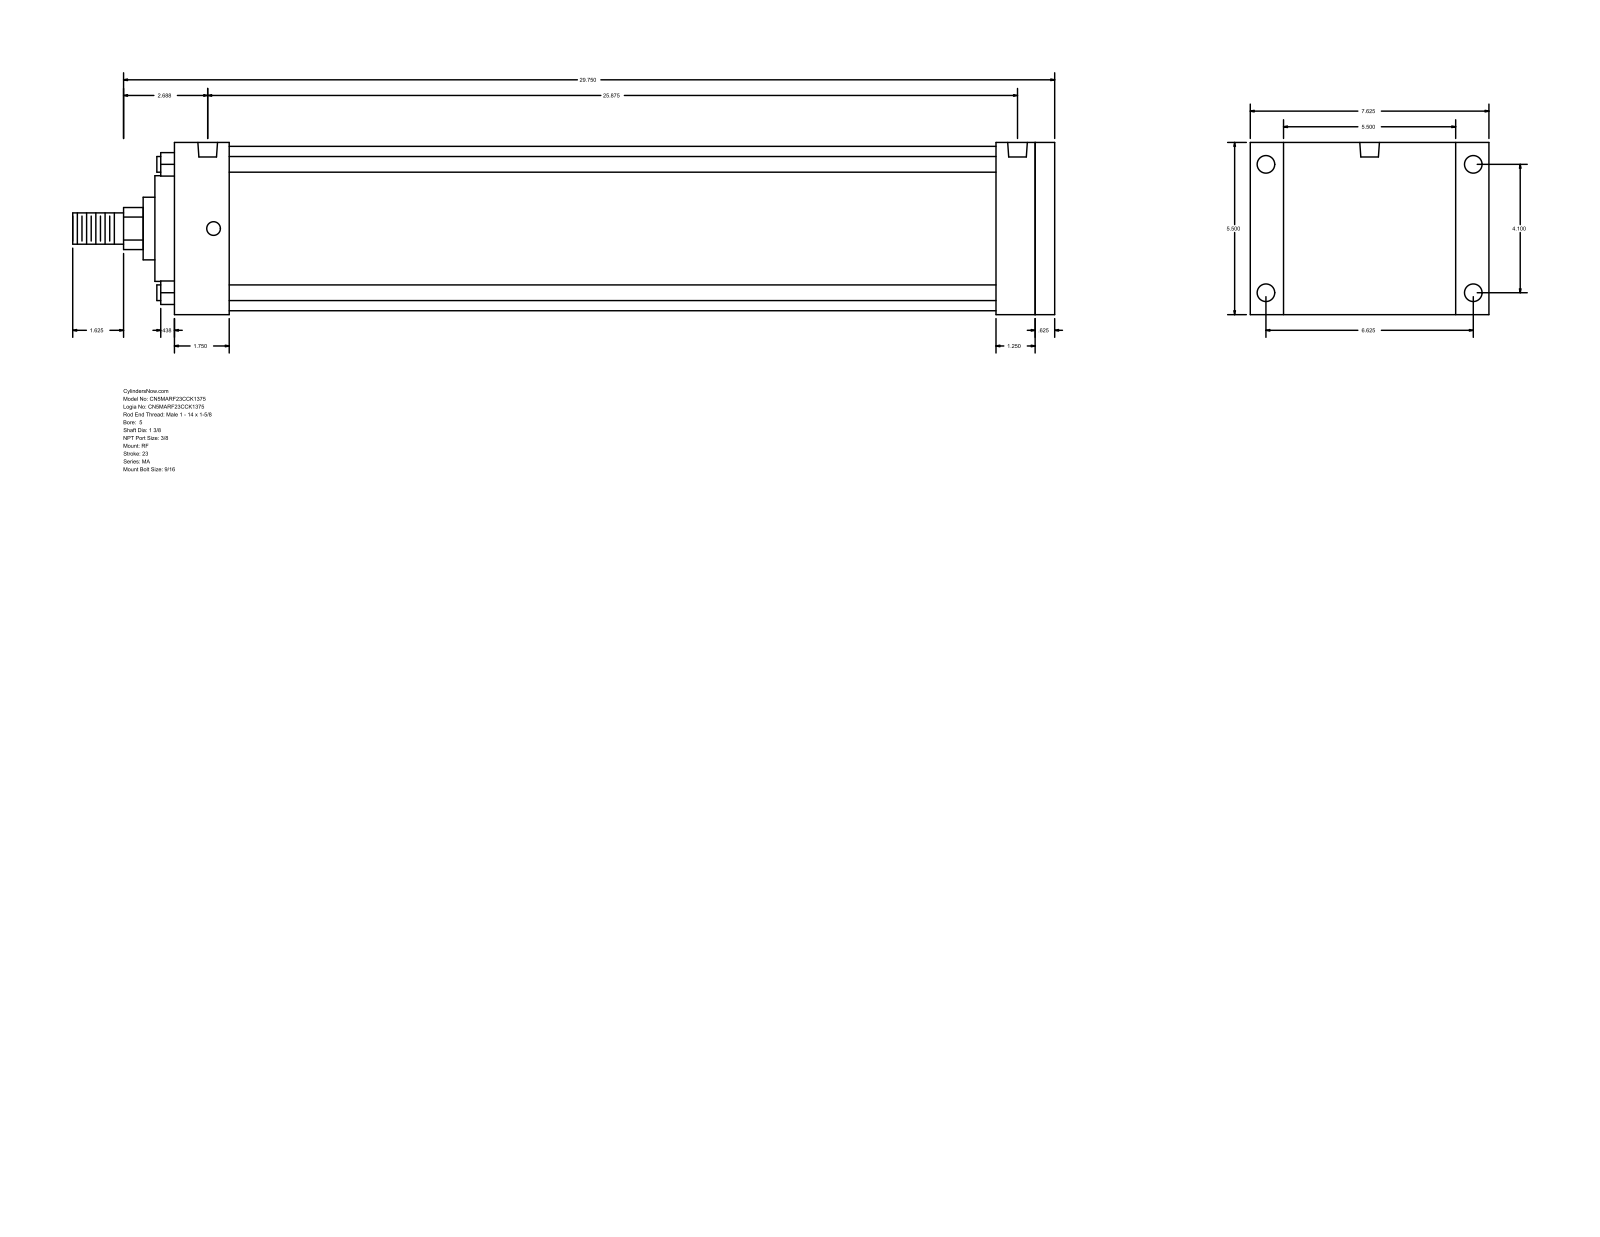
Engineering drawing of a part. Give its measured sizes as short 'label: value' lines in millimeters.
name: MA_RF__0500_1.375
written by: GSSL Pune (CONFIG_CONTROL_DESIGN)
unit: mm
bodies: 0 solids, 94 faces (65 planar, 29 cylindrical, 0 other)
size: 796.92 × 193.68 × 139.7
holes: 4× ⌀11.11, 4× ⌀14.29, 2× ⌀15.93
bosses: 4× ⌀12.7, 1× ⌀133.35, 1× ⌀85.72, 1× ⌀50.8, 1× ⌀34.92, 1× ⌀25.4
rounds: 1× R17.06
face distances: 139.7, 714.38, 15.88, 698.5, 44.45, 654.05, 669.93, 666.75, 622.3, 31.75
hole spacings: 104.14, 168.28, 197.9, 647.7, 4.76, 4.77, 652.46, 652.47
